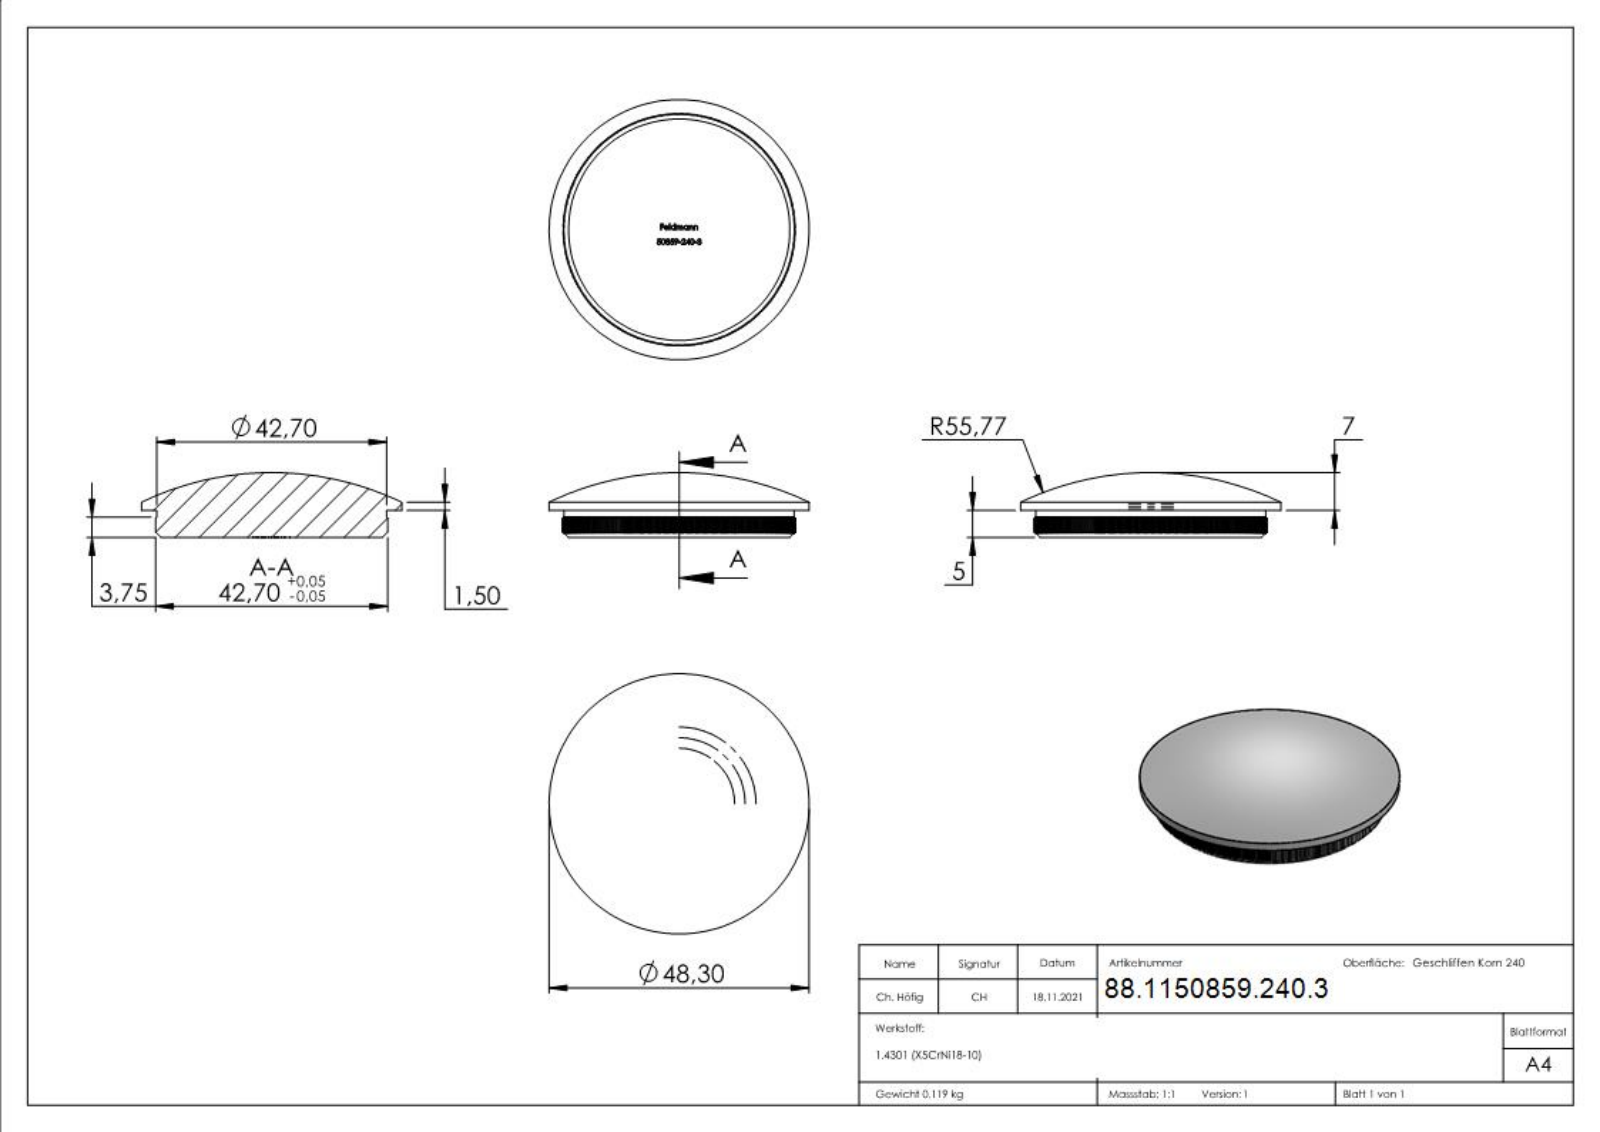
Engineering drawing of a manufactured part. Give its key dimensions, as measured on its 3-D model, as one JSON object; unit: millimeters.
{"part_name": "50859-240-3", "step_written_by": "SolidWorks 2018 (CONFIG_CONTROL_DESIGN)", "units": "millimeters", "bodies": {"solids": 1, "faces": 1901, "planar": 949, "cylindrical": 412, "other": 540}, "overall_size": [48.3, 48.3, 12], "volume_mm3": 15040, "surface_area_mm2": 4881, "round_bosses_or_shafts": [[48.3, 1], [42.7, 1]], "partial_cylinders_radius": [[21.55, 1]], "face_to_face_distances": [5, 21.34, 21.36, 21.38, 21.32, 4.9, 2.75, 0.31, 2.47, 1.01]}
